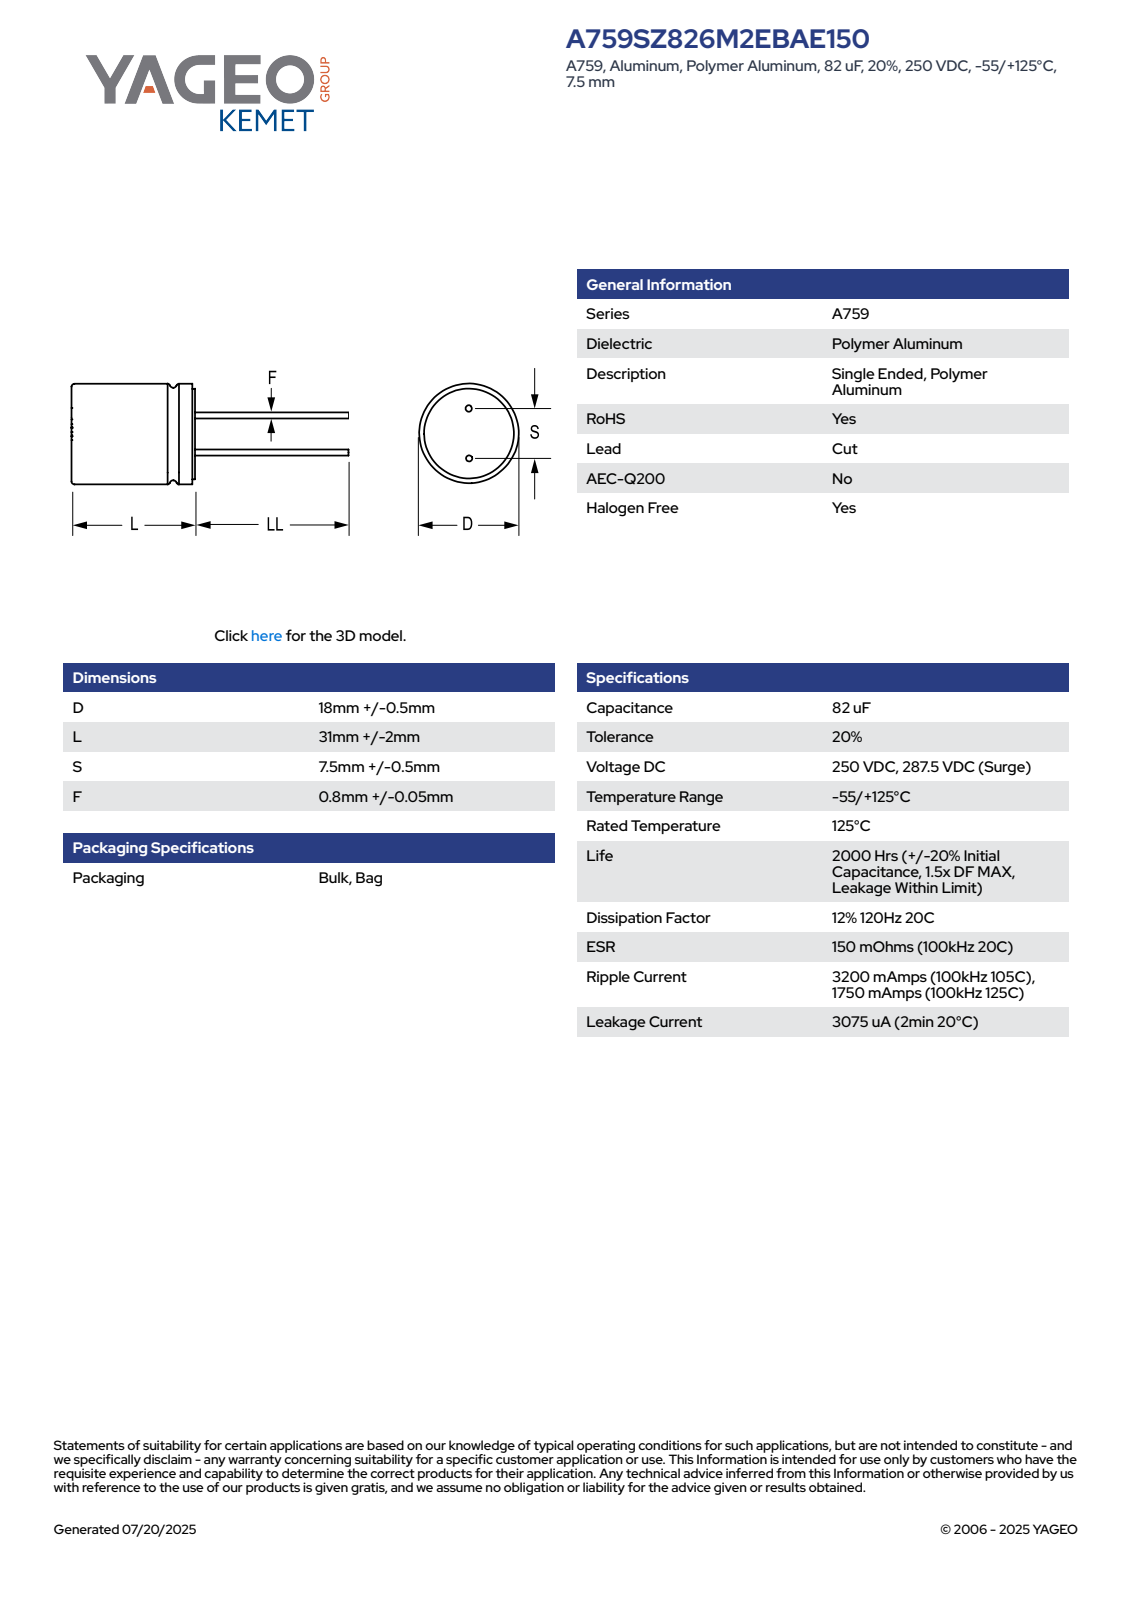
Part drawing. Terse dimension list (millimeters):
name: CAR_KPC_18X31_D18.5L33S7.5LL5.5F0.85
written by: SolidWorks 2021 (AUTOMOTIVE_DESIGN)
unit: mm
bodies: 4 solids, 78 faces (62 planar, 10 cylindrical, 6 other)
size: 38.51 × 18.5 × 18.5
volume: 8 823 mm³; area: 2 554 mm²
bosses: 2× ⌀0.85, 1× ⌀18.5, 1× ⌀16.61
face distances: 33, 32.85, 32.86, 33.01, 38.51, 38.5, 5.65, 5.5, 2.38, 0.65
